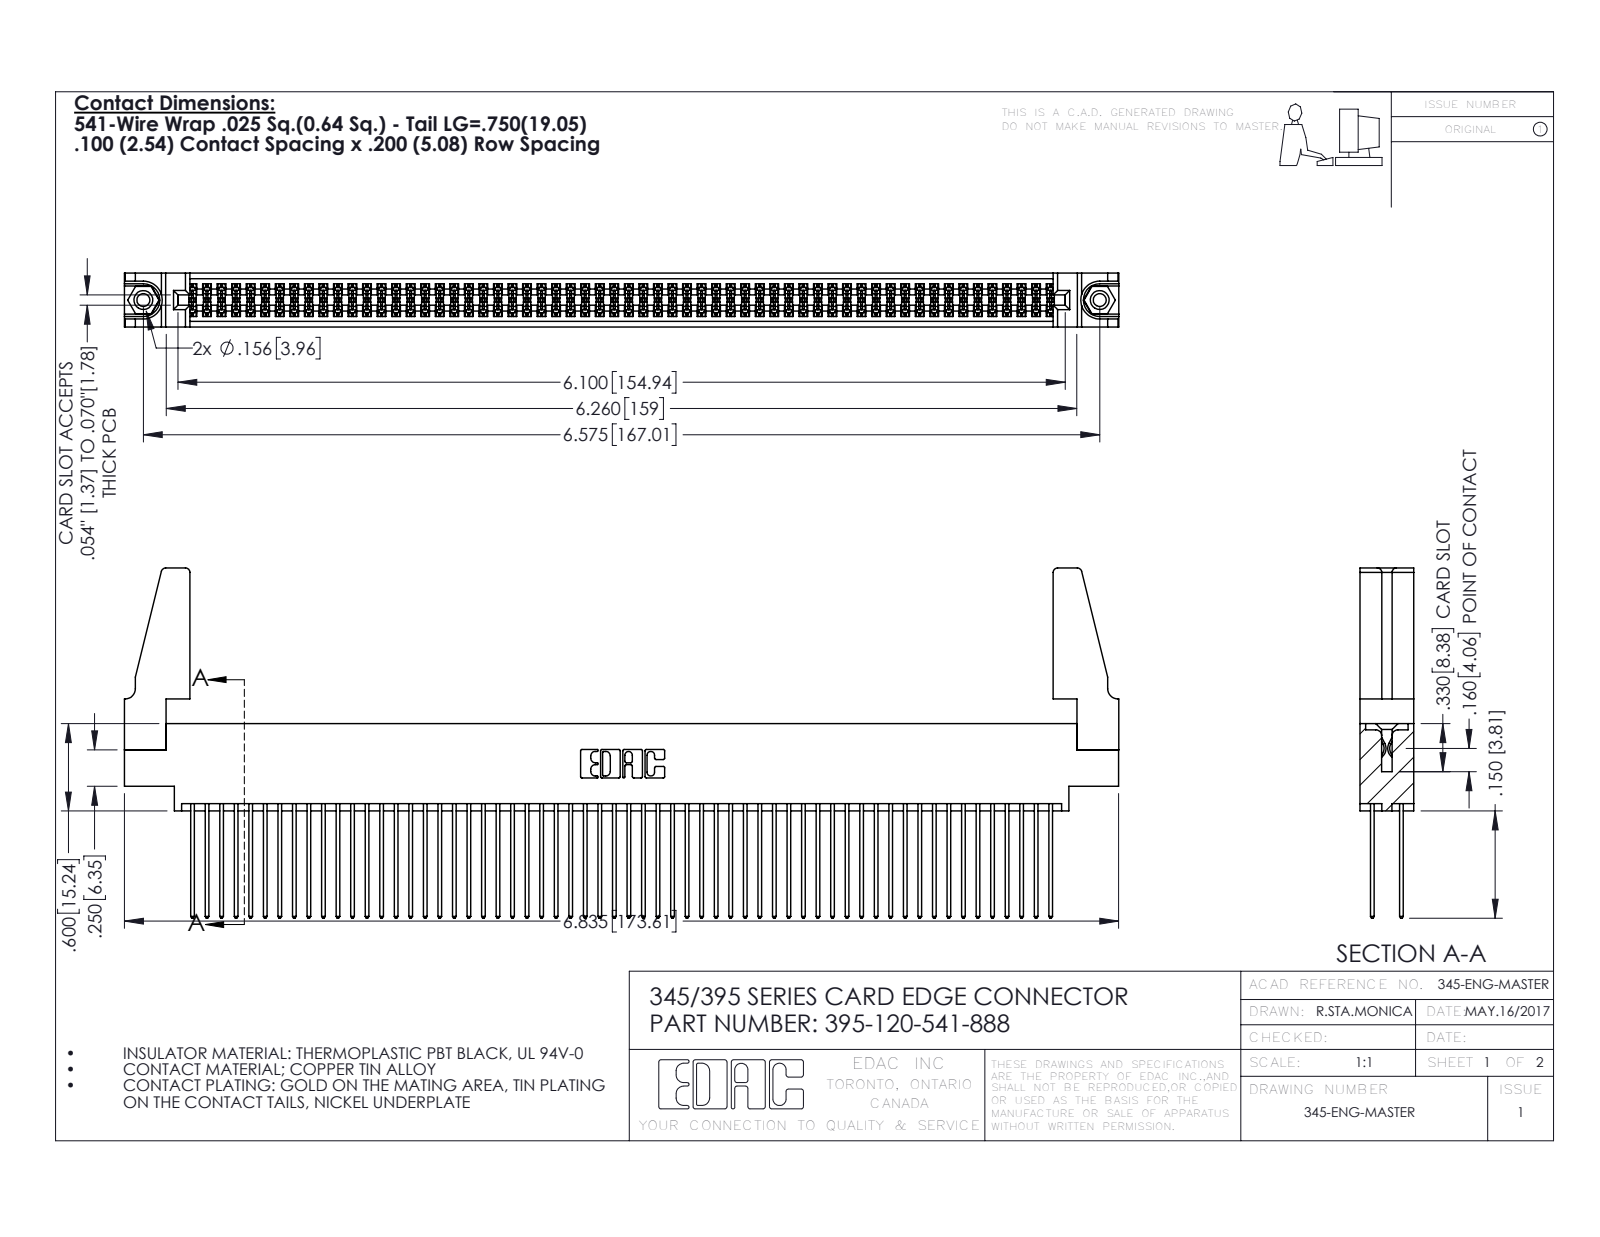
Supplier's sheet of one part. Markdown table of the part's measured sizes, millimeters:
| quantity | value |
| --- | --- |
| part name | 345-250-001_345-250-001-102; 345-292-001_345-293-141; 345-220-078_345-220-088; 345 Part_0.170 Offset - 0.156 Dia-TH (+1 more) |
| STEP written by | SolidWorks 2016 (CONFIG_CONTROL_DESIGN) |
| units | millimeters |
| bodies | 125 solids, 6254 faces (4116 planar, 2122 cylindrical, 16 other) |
| overall size | 173.6 × 61.1 × 9.4 |
| volume | 20 860 mm³ |
| surface area | 32 880 mm² |
| round holes (diameter × count) | 2.3 × 2, 3.2 × 2, 4 × 2, 1.6 × 1 |
| round bosses / shafts (diameter × count) | 3.9 × 2 |
| partial cylindrical surfaces (radius × count) | 0.2 × 180, 0.3 × 120, 0.3 × 22, 0.8 × 8, 0.2 × 6, 0.8 × 6, 0.7 × 3, 0.4 × 2 |
| main face-to-face distances | 1.8, 7.6, 2.5, 6.9, 0.6, 5.1, 9.4, 5.7, 4.4, 3.8 |
| hole center spacings | 6.9, 161, 167 |
